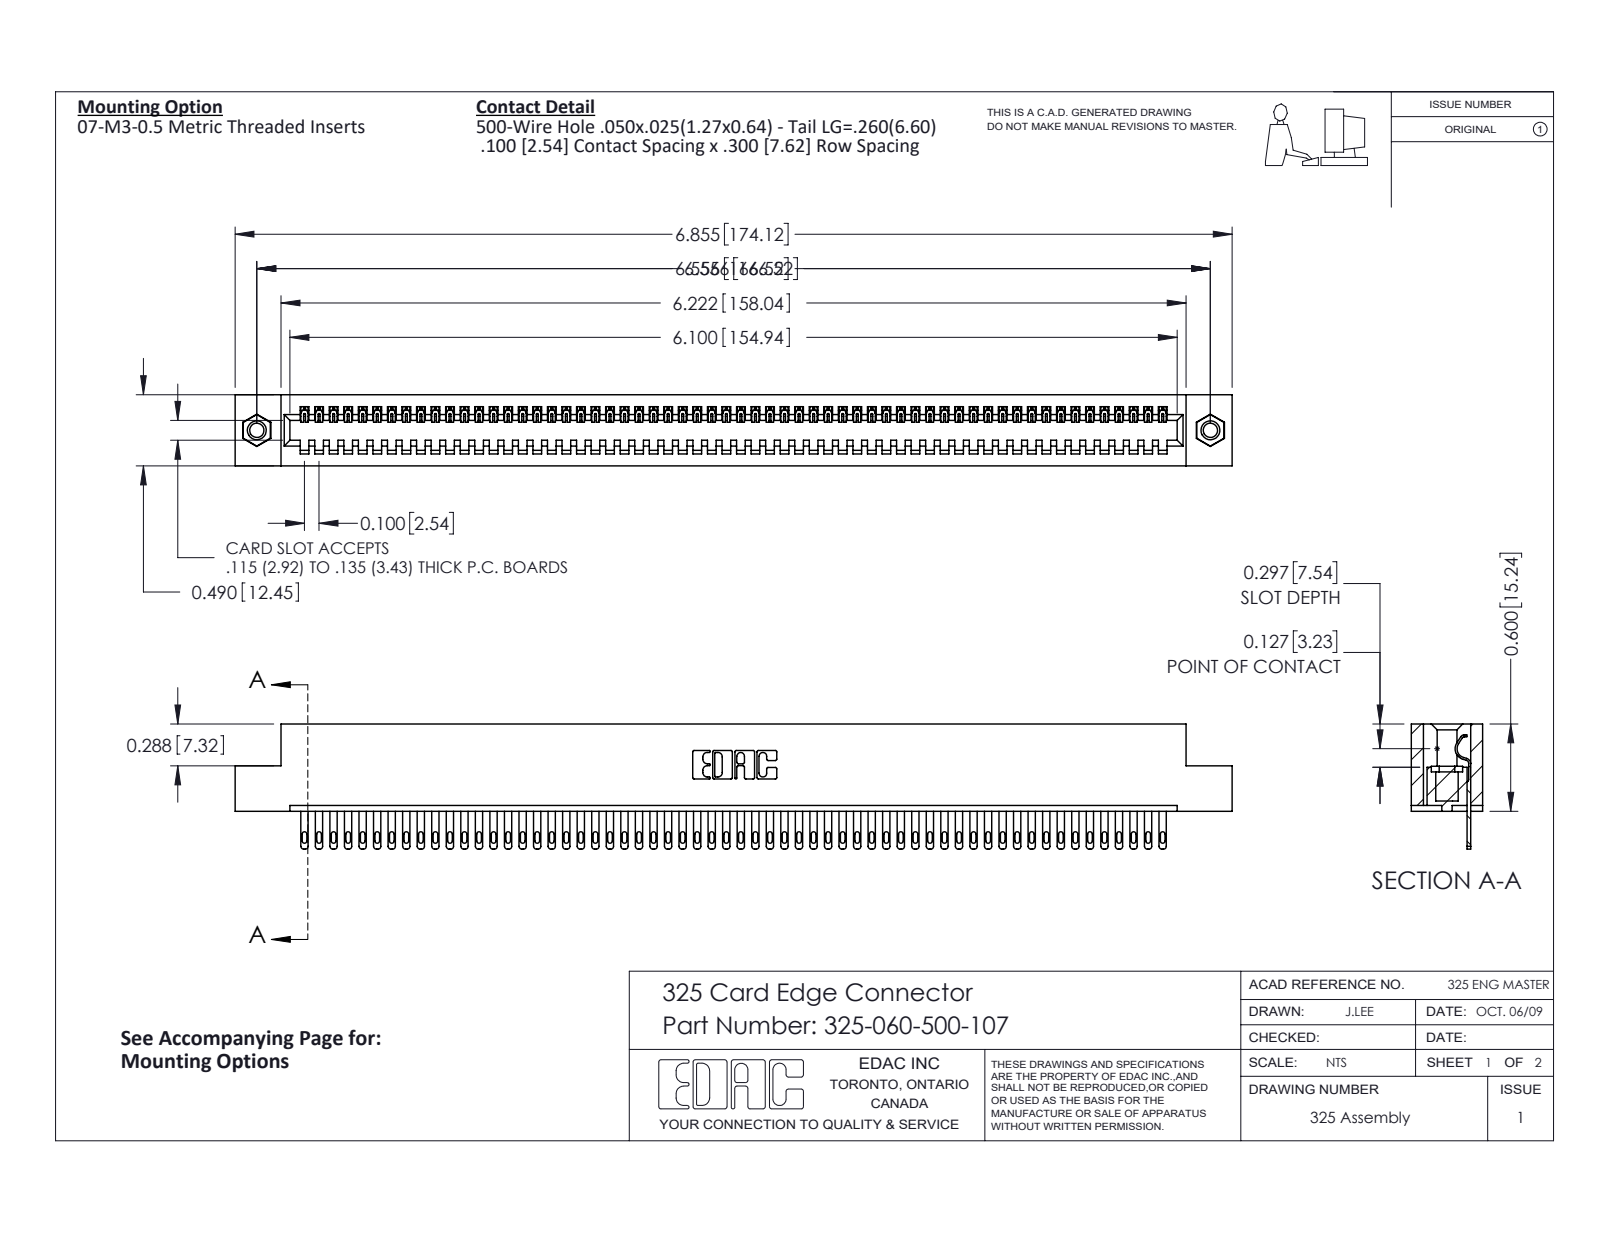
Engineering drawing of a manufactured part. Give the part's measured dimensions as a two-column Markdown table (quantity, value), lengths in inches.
| quantity | value |
| --- | --- |
| part name | 325-060-500-107; 345-250-001_345-250-005-103; 325 Part_TI; 325-292-001_325-293-100 |
| STEP written by | SolidWorks 2016 (CONFIG_CONTROL_DESIGN) |
| units | inches |
| bodies | 63 solids, 3414 faces (2262 planar, 1136 cylindrical, 16 other) |
| overall size | 6.855 × 0.86 × 0.49 |
| volume | 1.359 in³ |
| surface area | 38.44 in² |
| round holes (diameter × count) | 0.098 × 2, 0.125 × 2, 0.16 × 2 |
| round bosses / shafts (diameter × count) | 0.155 × 2 |
| partial cylindrical surfaces (radius × count) | 0.006 × 120, 0.016 × 120, 0.02 × 120, 0.01 × 22, 0.007 × 6, 0.031 × 6, 0.026 × 3, 0.014 × 1 |
| main face-to-face distances | 0.083, 0.407, 0.49, 0.3, 0.107, 0.383, 0.025, 0.325, 0.56, 0.263 |
| hole center spacings | 6.556 |
